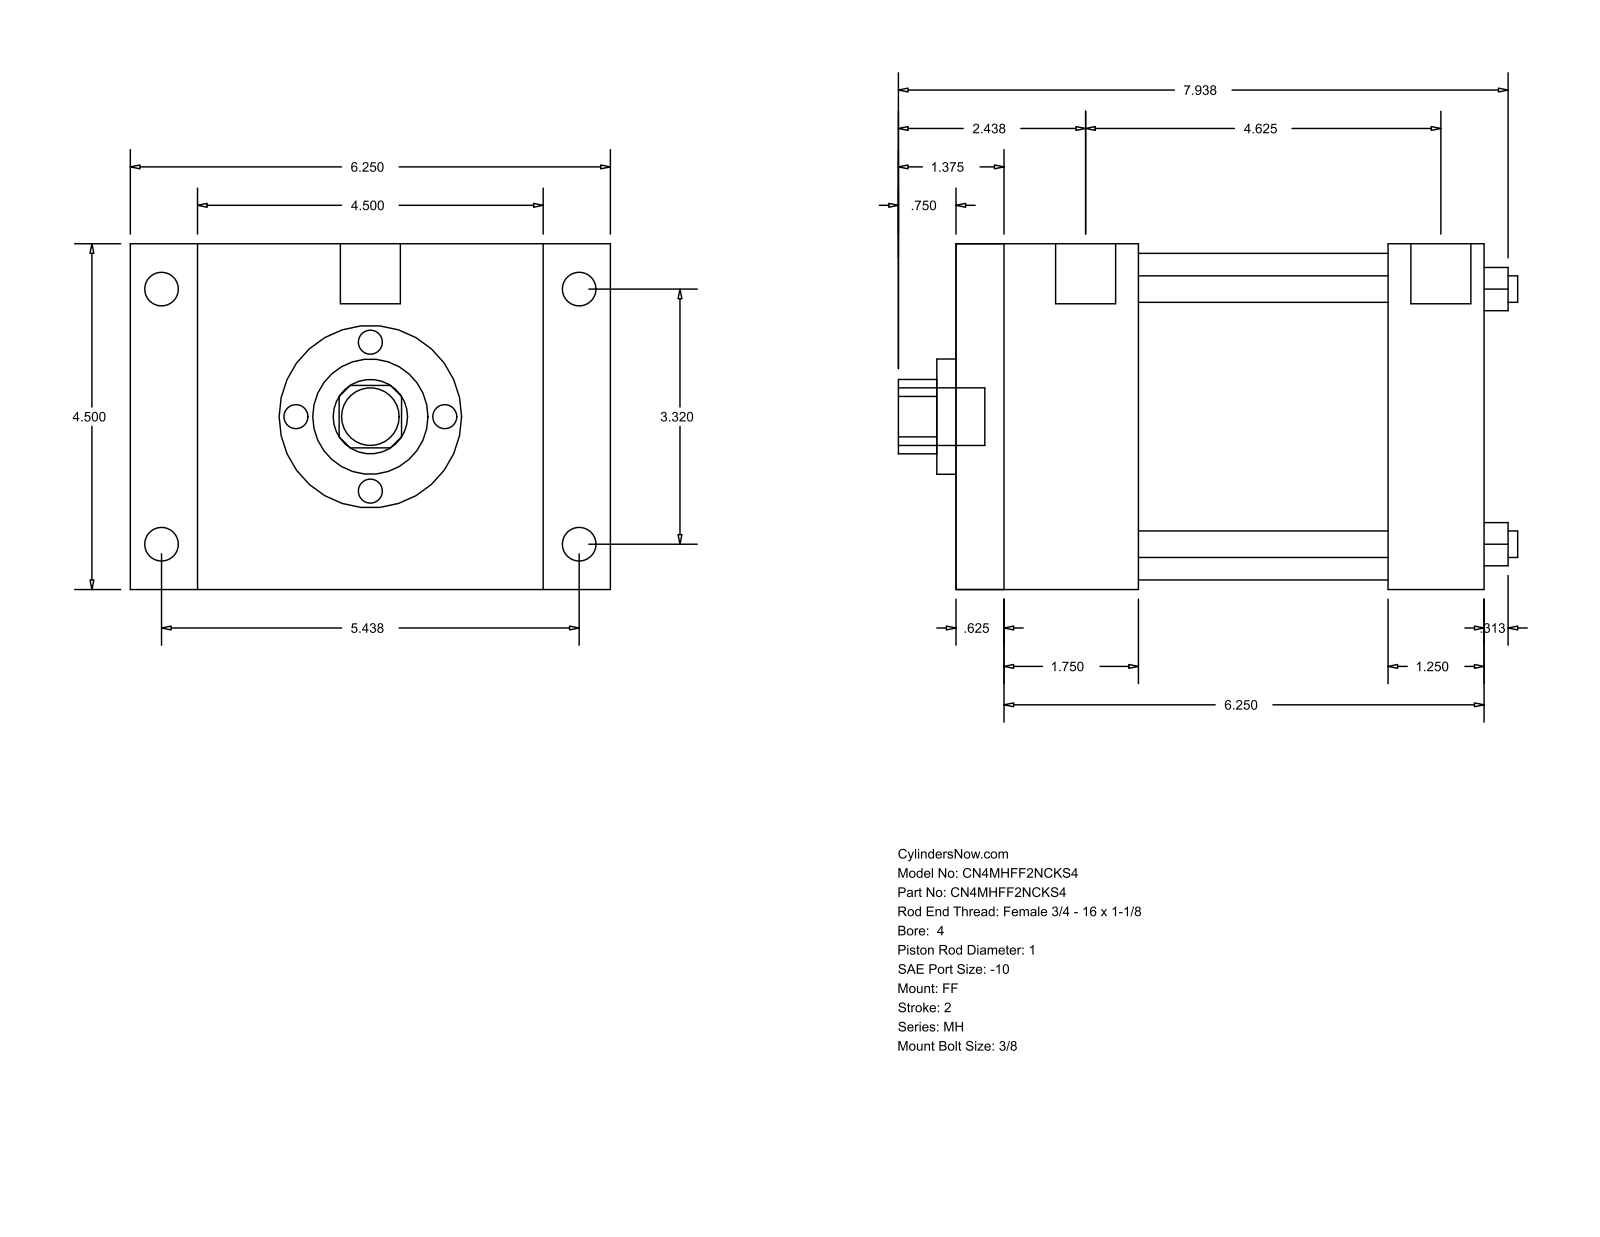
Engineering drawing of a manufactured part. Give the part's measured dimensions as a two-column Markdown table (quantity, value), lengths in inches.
| quantity | value |
| --- | --- |
| part name | MH_FF__0400_1 |
| STEP written by | GSSL Pune (CONFIG_CONTROL_DESIGN) |
| units | inches |
| bodies | 0 solids, 92 faces (64 planar, 28 cylindrical, 0 other) |
| overall size | 8.063 × 6.25 × 4.5 |
| round holes (diameter × count) | 0.345 × 4, 1 × 1, 1.5 × 1, 4.25 × 1 |
| round bosses / shafts (diameter × count) | 0.438 × 4, 0.344 × 4, 0.781 × 2, 0.75 × 1 |
| partial cylindrical surfaces (radius × count) | 0.484 × 1 |
| main face-to-face distances | 4.5, 6.875, 6.25, 0.625, 2.375, 1.75, 5.625, 5, 3.25, 1.25 |
| hole center spacings | 2.347, 3.32, 4.695 |
